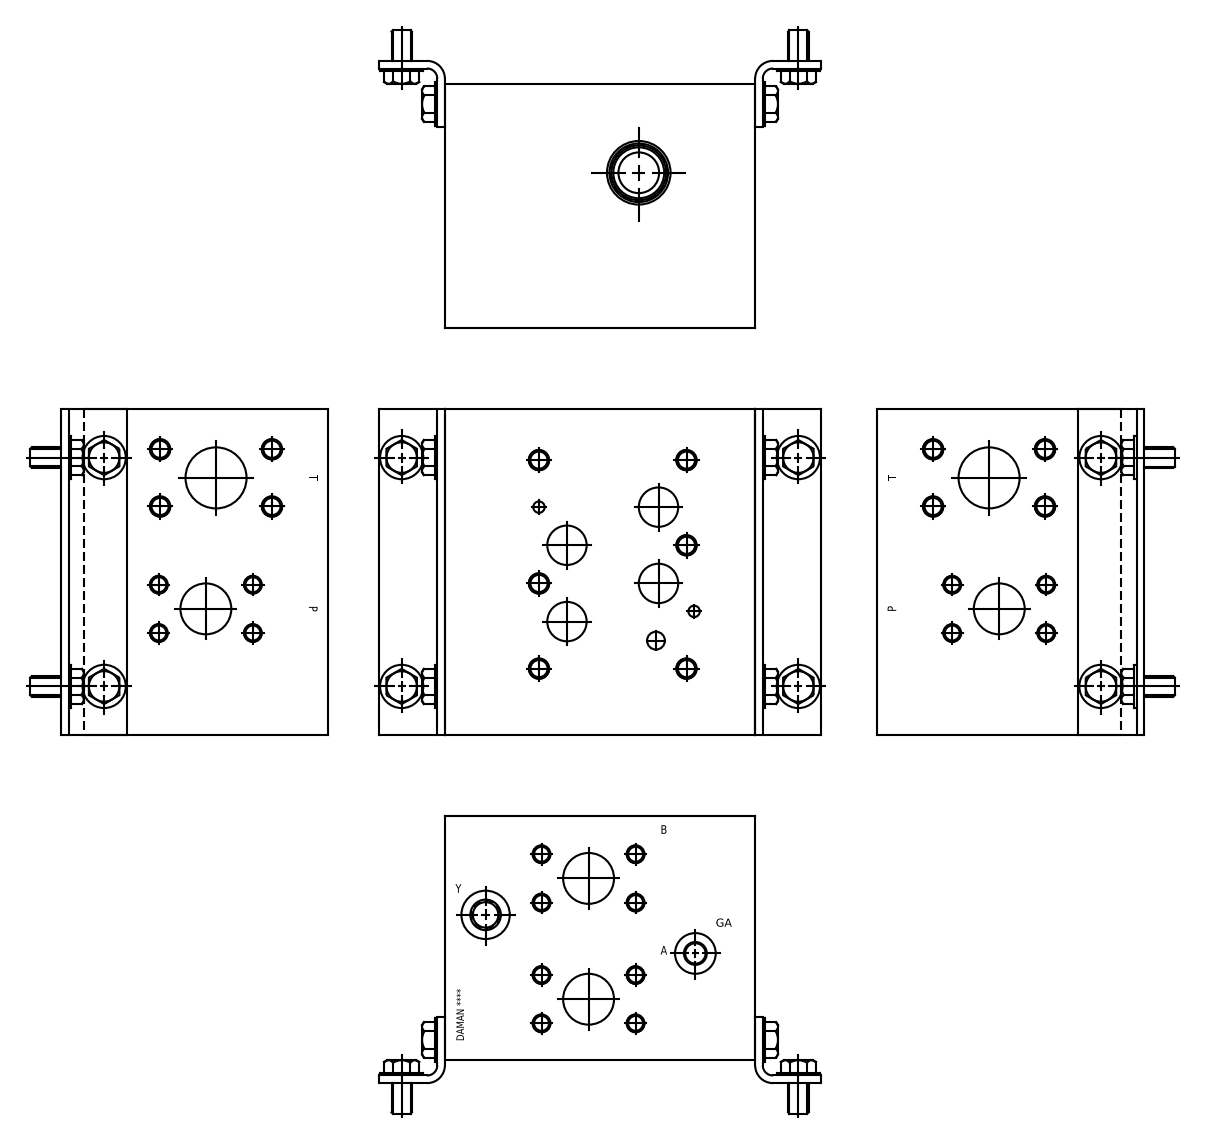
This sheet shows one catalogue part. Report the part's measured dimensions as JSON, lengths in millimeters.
{"part_name": "Part_AD08HP015F~S_3D", "step_written_by": "Autodesk Inventor 2021 (AUTOMOTIVE_DESIGN)", "units": "millimeters", "bodies": {"solids": 1, "faces": 672, "planar": 376, "cylindrical": 97, "other": 199}, "overall_size": [203.2, 193.68, 152.4], "volume_mm3": 5709000, "surface_area_mm2": 260980, "round_holes": [[11.13, 16], [9.35, 15], [12.7, 13], [10.72, 12], [24.61, 4], [31.75, 4], [7.14, 2], [12.29, 1], [12.9, 1], [14.27, 1], [14.53, 1], [17.5, 1]], "face_to_face_distances": [152.4, 193.68, 203.2, 0.79, 202.41, 30.23, 28.45, 163.45, 140.16, 139.37], "hole_center_spacings": [33.01, 30.18, 58.72, 66.02, 75.41, 95.14, 67.09, 95.58]}
